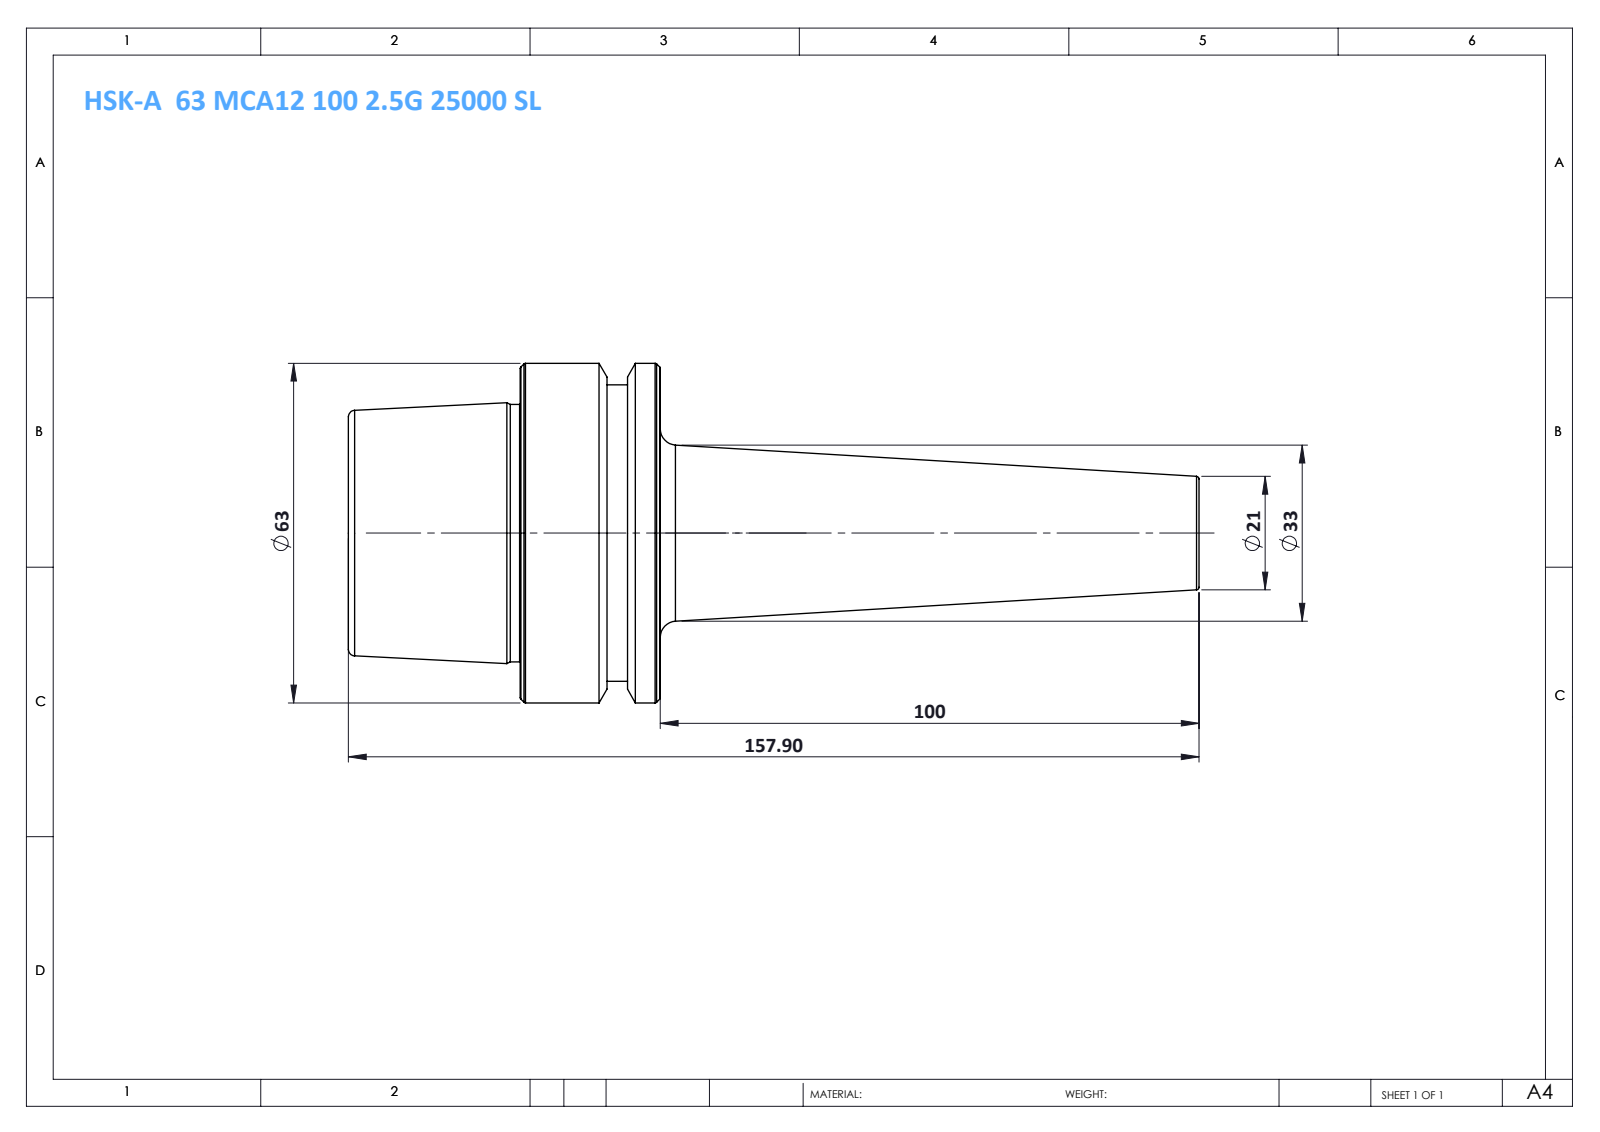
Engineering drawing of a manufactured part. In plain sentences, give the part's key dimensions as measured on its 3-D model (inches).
The part is named "HSK-A 63 MCA12 100 2.5G 25000 SL". Its 3-D file was written by "SolidWorks 2014 (CONFIG_CONTROL_DESIGN)". It is 1 solid with 46 faces: 6 planar, 8 cylindrical and 32 other. Overall it measures 6.217 by 2.48 by 2.48 inches. Its volume is 11.65 cubic inches and its surface area 38 square inches. Round bosses or shafts: 1 of diameter 2.48, 1 of diameter 2.165, 1 of diameter 1.881. The main face-to-face distances are 2.28, 1.024, 1.256, 3.937, 4.961, 6.217, 4.177, 0.24, 0.783, 2.039.
